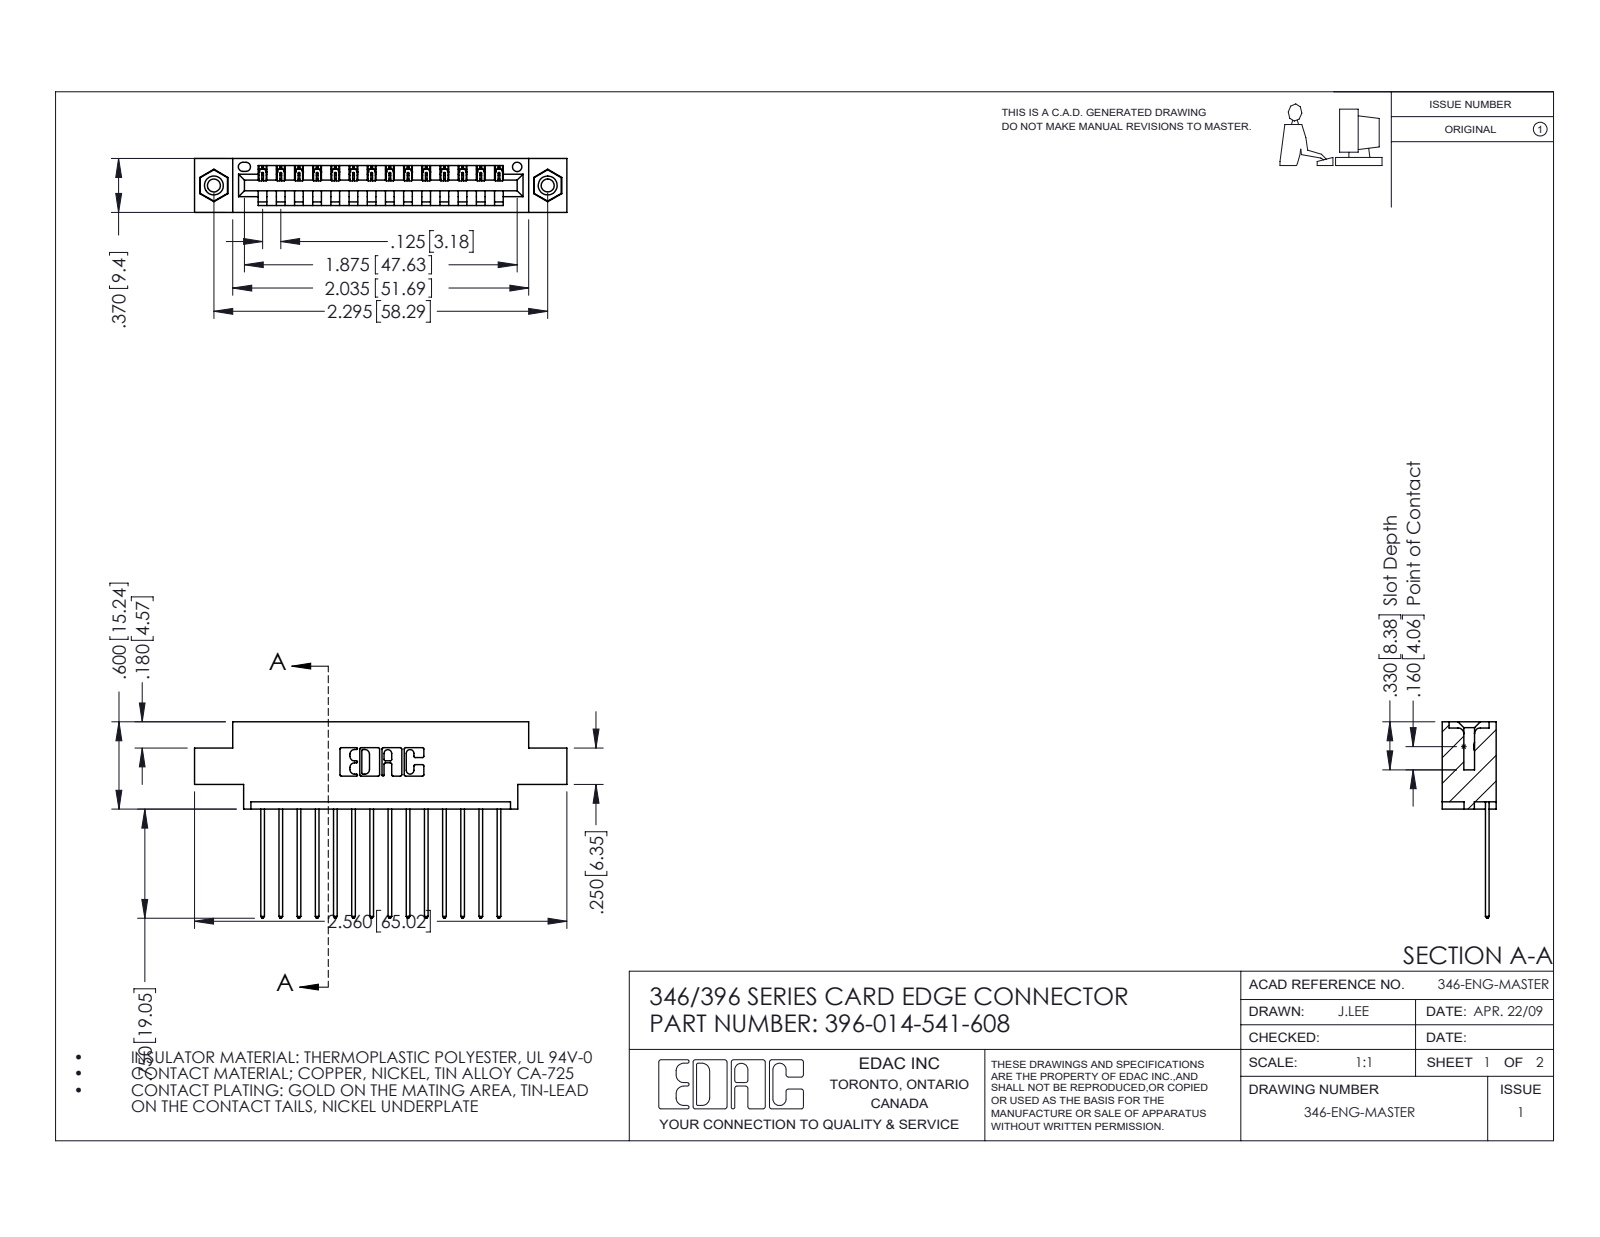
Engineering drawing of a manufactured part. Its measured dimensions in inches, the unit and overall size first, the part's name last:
Units: inches
Overall size (bounding box): 2.56 × 1.35 × 0.37
Round holes (diameter × count): ⌀0.089 ×2, ⌀0.125 ×2, ⌀0.156 ×2, ⌀0.064 ×1
Round bosses / shafts (diameter × count): ⌀0.155 ×2
Partial cylindrical surfaces — rounded edges, fillets, slot ends (radius × count): R0.006 ×28, R0.01 ×28, R0.01 ×22, R0.007 ×6, R0.031 ×6, R0.026 ×3, R0.031 ×2, R0.04 ×2
Main face-to-face distances: 0.048, 0.322, 0.37, 0.25, 0.072, 0.298, 0.025, 0.222, 0.148, 0.1
Hole centre spacings: 0.246, 2.089, 2.295
Volume: 0.361 in³ · Surface area: 11.7 in²
Bodies: 17 solids, 998 faces (672 planar, 310 cylindrical, 16 other)
Part name (STEP PRODUCT): 396-014-541-608; 345-250-001_345-250-003-102; 345-292-001_345-293-141; 346 Part_0.170 Offset - 0.156 Dia-TI
STEP written by: SolidWorks 2016 (CONFIG_CONTROL_DESIGN)
